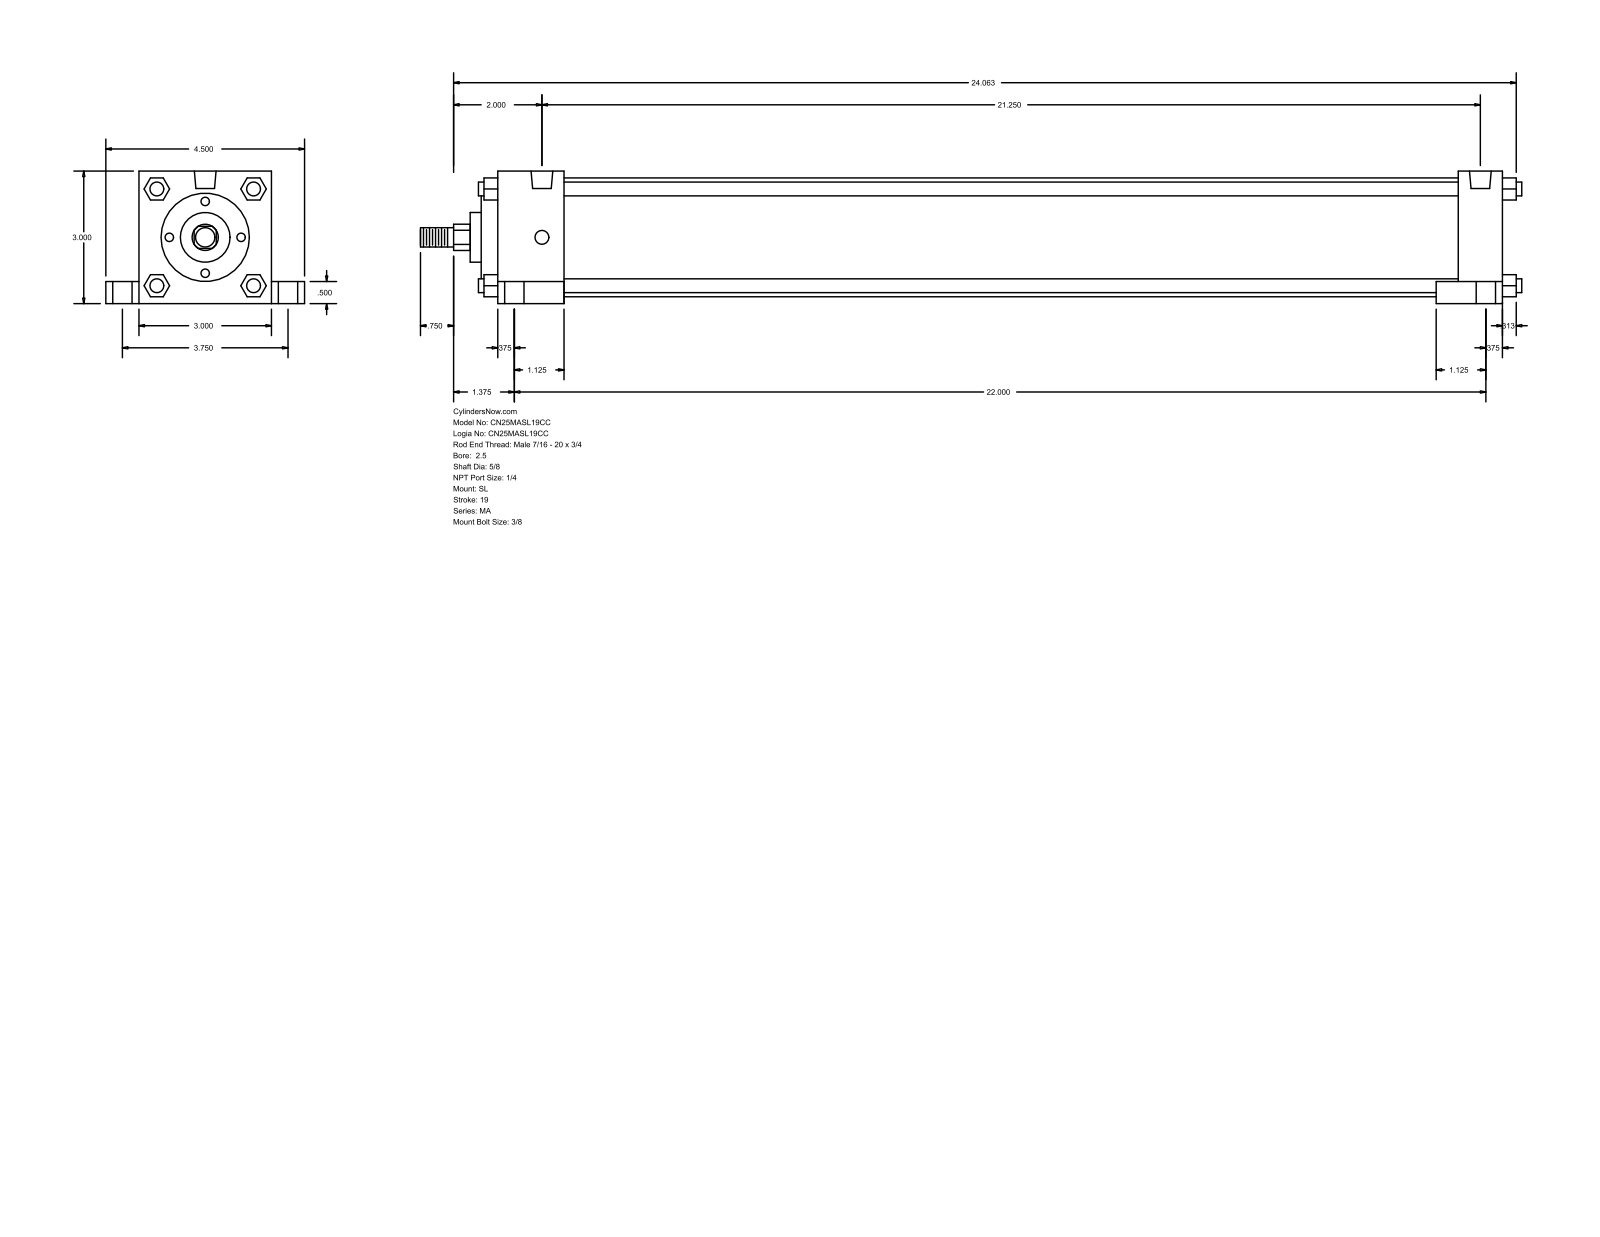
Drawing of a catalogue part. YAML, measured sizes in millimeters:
part_name: "MA_SL__0250_0.625"
step_written_by: "GSSL Pune (CONFIG_CONTROL_DESIGN)"
units: millimeters
bodies: {solids: 0, faces: 150, planar: 113, cylindrical: 37, other: 0}
overall_size: [633.41, 114.3, 76.2]
round_holes:
  - {diameter: 7.94, count: 4}
  - {diameter: 11.11, count: 4}
  - {diameter: 17.46, count: 4}
  - {diameter: 12.49, count: 2}
round_bosses_or_shafts:
  - {diameter: 7.94, count: 4}
  - {diameter: 68.33, count: 1}
  - {diameter: 50.8, count: 1}
  - {diameter: 28.57, count: 1}
  - {diameter: 15.88, count: 1}
  - {diameter: 11.11, count: 1}
partial_cylinders:
  - {radius: 7.54, count: 1}
face_to_face_distances: [76.2, 577.85, 12.7, 514.35, 25.4, 38.1, 539.75, 552.45, 19.05, 63.5]
hole_center_spacings: [47.73, 50.2, 95.24, 539.75, 545.01, 557.67, 558.81, 566.87]
